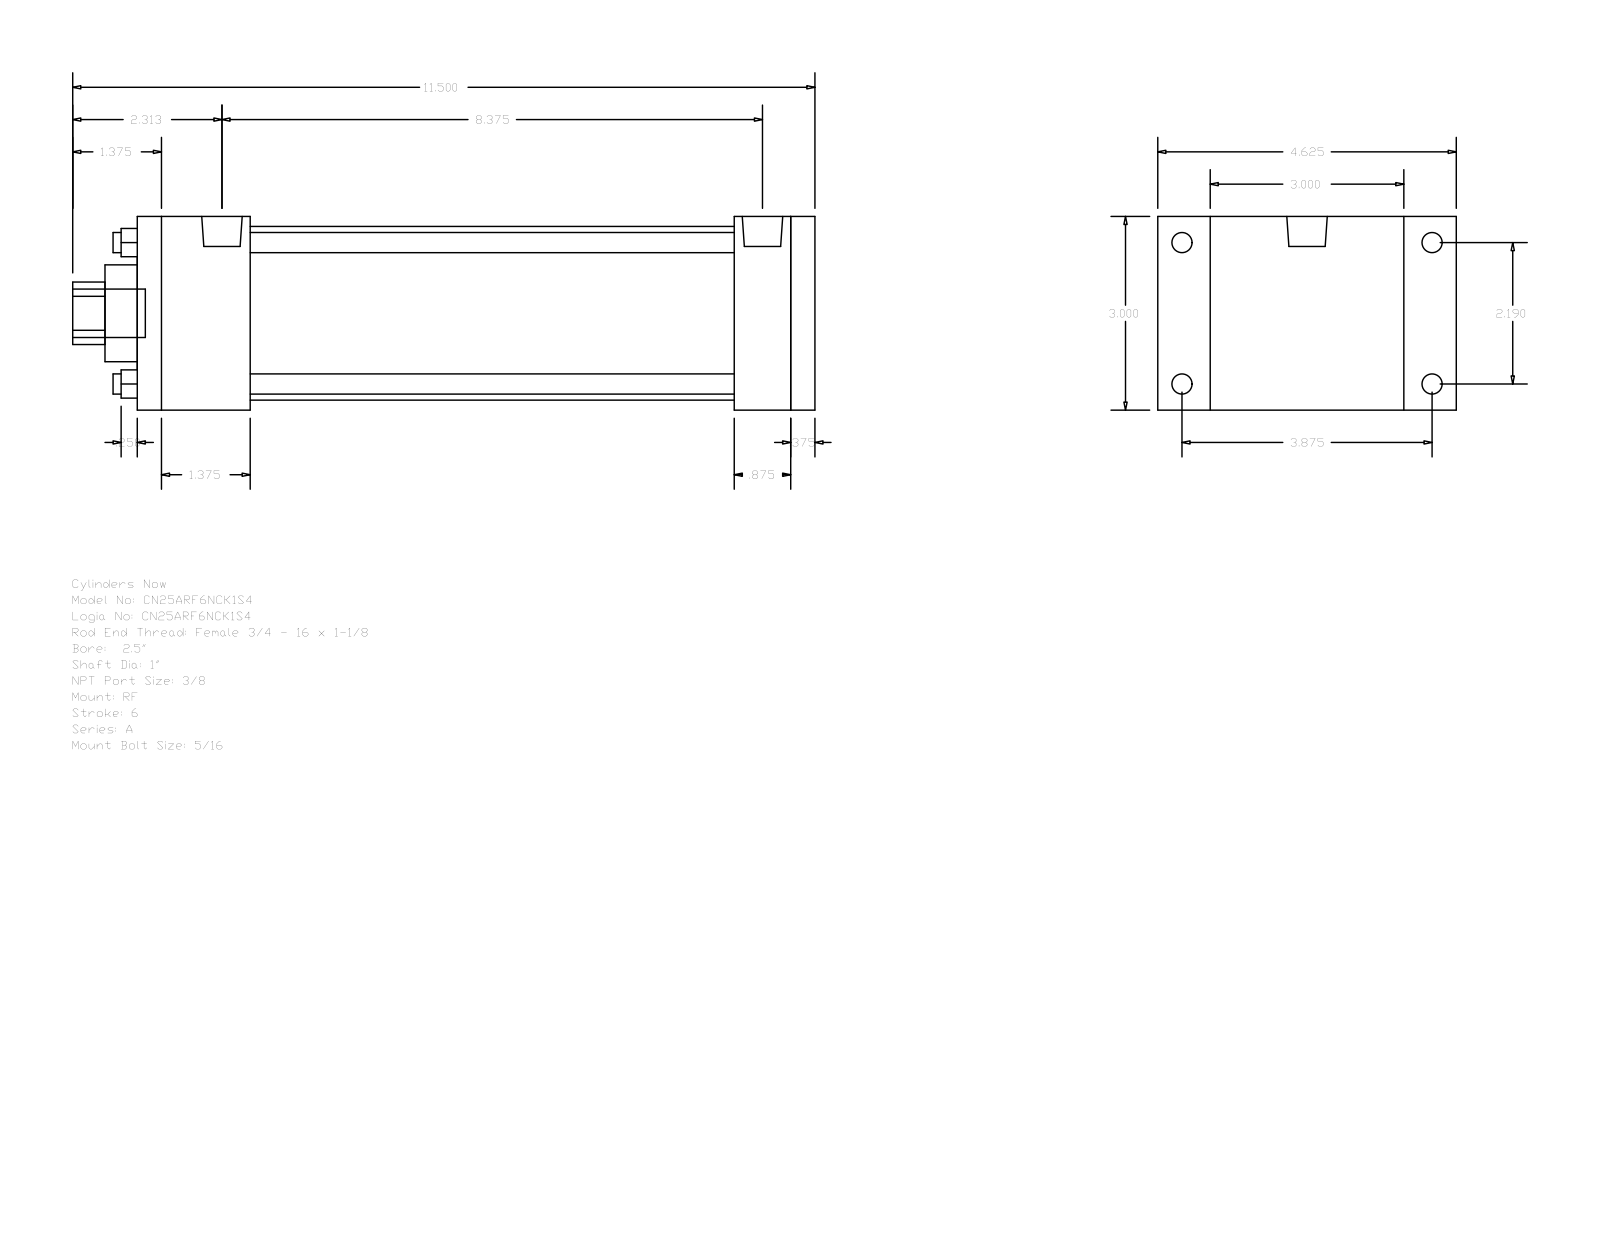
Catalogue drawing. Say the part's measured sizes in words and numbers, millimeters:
The part is named "A_RF__0250_1". Its 3-D file was written by "GSSL Pune (CONFIG_CONTROL_DESIGN)". It is 0 solids with 92 faces: 64 planar, 28 cylindrical and 0 other. Overall it measures 292.1 by 117.47 by 76.2 millimeters. Round holes: 4 of diameter 7.94, 1 of diameter 25.4, 1 of diameter 38.1, 1 of diameter 68.33. Round bosses or shafts: 4 of diameter 7.94, 4 of diameter 5.56, 2 of diameter 15.93, 1 of diameter 19.05. Partial cylindrical surfaces (rounded edges, fillets, slot ends): 1 of radius 12.29. The main face-to-face distances are 76.2, 266.7, 9.53, 257.17, 44.45, 234.95, 190.5, 212.72, 222.25, 22.22. The hole center spacings are 39.33, 55.62, 78.66.
